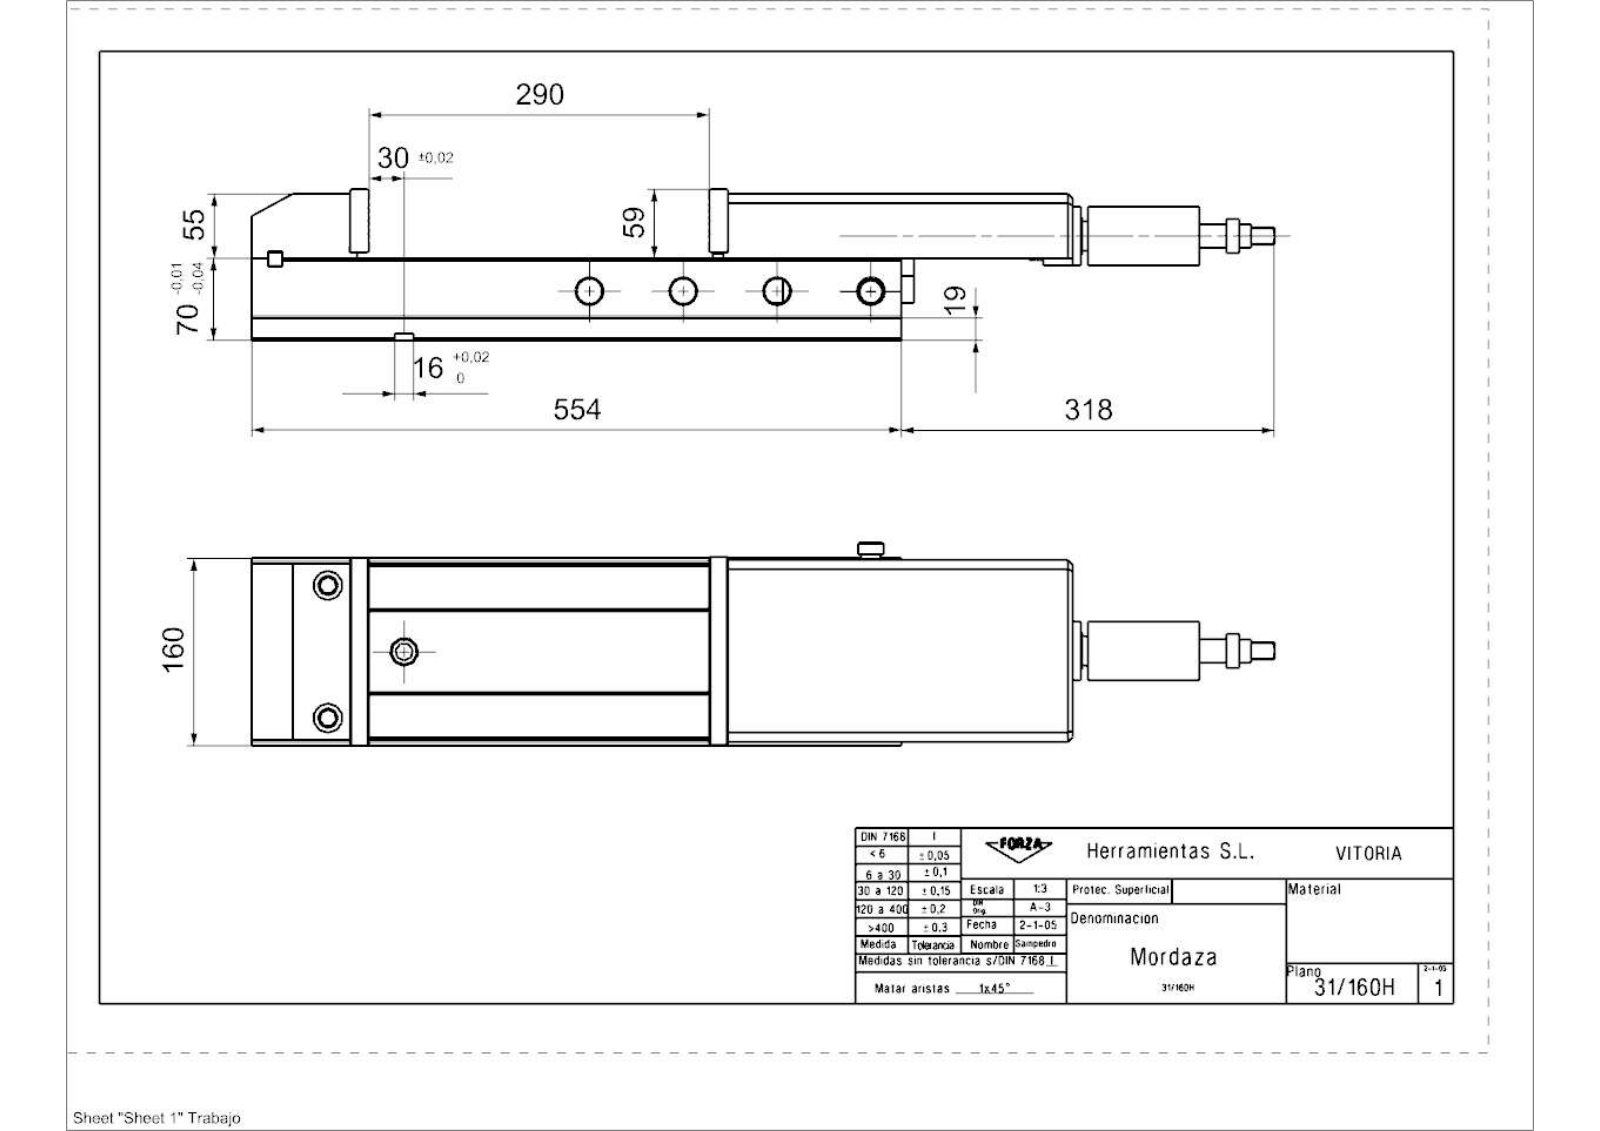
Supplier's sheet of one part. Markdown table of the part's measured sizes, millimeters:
| quantity | value |
| --- | --- |
| part name | 31_160H_Mordaza |
| STEP written by | SIEMENS PLM Software NX 9.0 (CONFIG_CONTROL_DESIGN) |
| units | millimeters |
| bodies | 14 solids, 478 faces (311 planar, 94 cylindrical, 73 other) |
| overall size | 872 × 173 × 129 |
| volume | 7 274 000 mm³ |
| surface area | 814 645 mm² |
| round holes (diameter × count) | 22 × 8, 5.19 × 6, 6.99 × 4, 9 × 4, 14 × 4, 15 × 4, 17 × 4, 8.78 × 2, 11 × 2, 12.38 × 2, 14.38 × 2, 25 × 2 |
| round bosses / shafts (diameter × count) | 50 × 1, 46 × 1, 41 × 1, 38 × 1, 37 × 1, 32 × 1, 29.5 × 1, 29 × 1 |
| partial cylindrical surfaces (radius × count) | 10 × 4, 2 × 2, 6.5 × 2, 8 × 2, 25 × 1, 32 × 1 |
| main face-to-face distances | 70, 125, 55, 41, 29, 96, 155, 5, 150, 1.5 |
| hole center spacings | 80, 41.48, 0.66, 4, 4.05, 17.03, 19.85, 25 |
